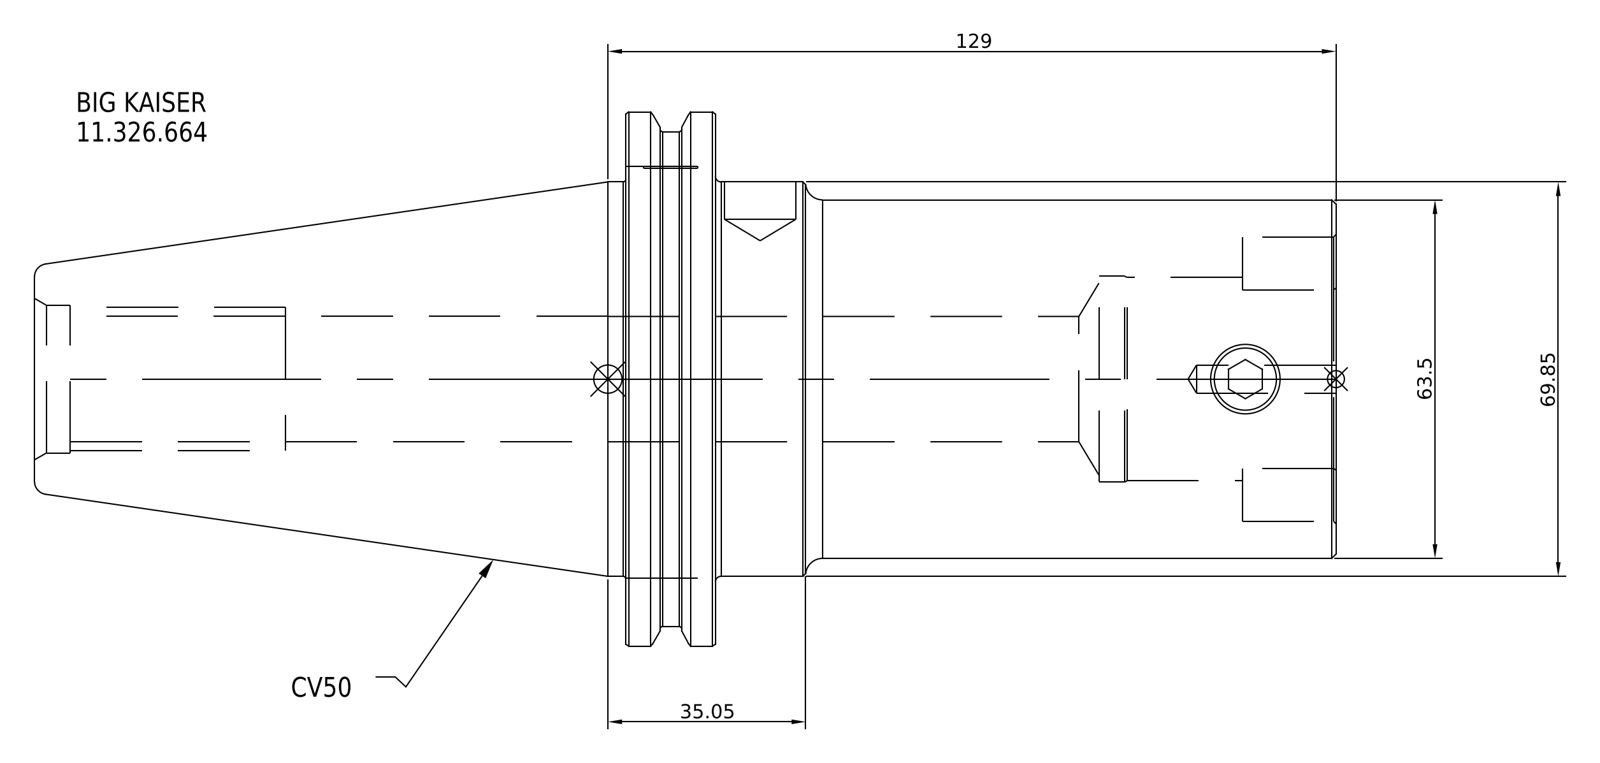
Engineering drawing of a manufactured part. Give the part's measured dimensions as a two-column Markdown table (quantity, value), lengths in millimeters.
| quantity | value |
| --- | --- |
| part name | 11.326.664 |
| STEP written by | SolidWorks 2021 (CONFIG_CONTROL_DESIGN) |
| units | millimeters |
| bodies | 1 solid, 16 faces (7 planar, 6 cylindrical, 3 other) |
| overall size | 230.6 × 98.43 × 98.43 |
| volume | 738 019 mm³ |
| surface area | 59 657 mm² |
| round bosses / shafts (diameter × count) | 98.43 × 1, 91.29 × 1, 69.85 × 1, 63.27 × 1 |
| main face-to-face distances | 17.55, 109.95, 127.5, 230.6, 120.65, 103.1, 94, 15.95, 33.5, 136.6 |
